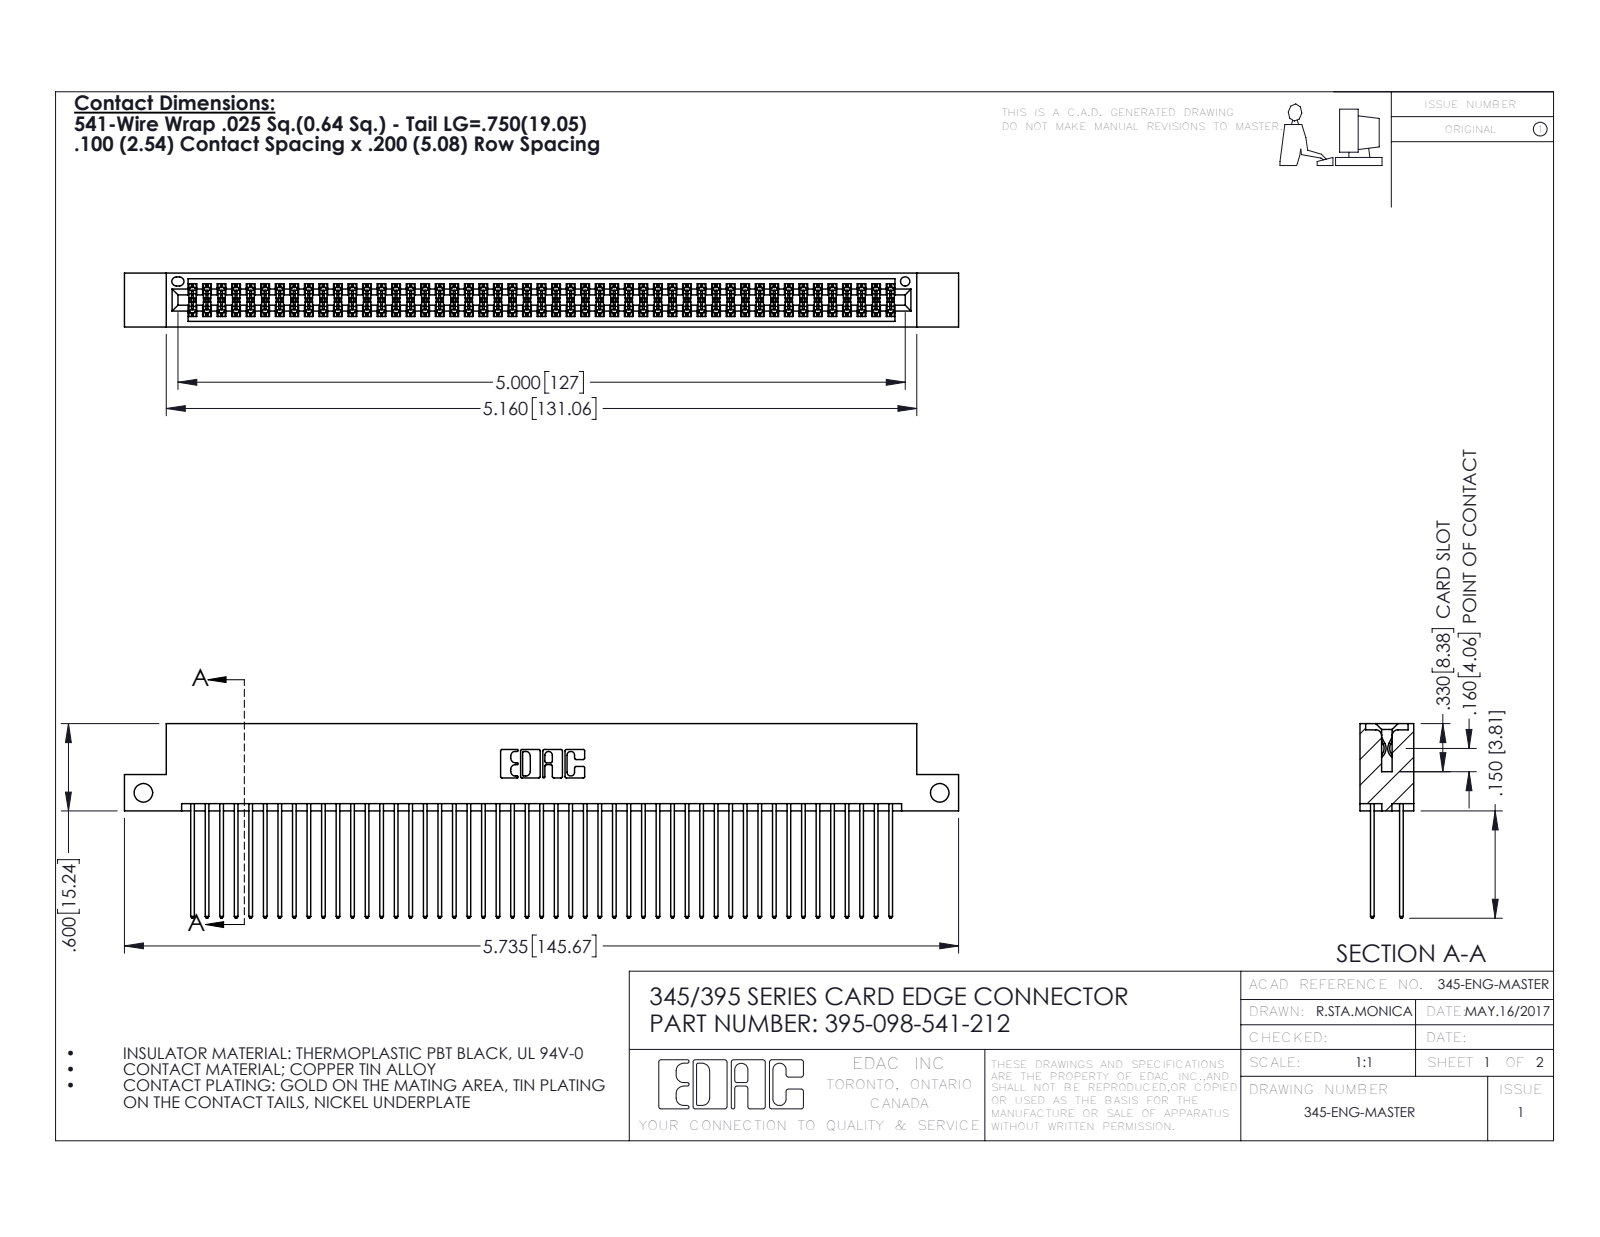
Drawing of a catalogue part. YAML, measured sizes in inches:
part_name: "345-292-001_345-293-141; 345 Part_Flush Mounting Lugs - Side Mount; 395-098-541-212"
step_written_by: "SolidWorks 2016 (CONFIG_CONTROL_DESIGN)"
units: inches
bodies: {solids: 99, faces: 5026, planar: 3314, cylindrical: 1712, other: 0}
overall_size: [5.735, 1.337, 0.37]
volume: 0.896
surface_area: 37.75
round_holes:
  - {diameter: 0.128, count: 2}
  - {diameter: 0.064, count: 1}
partial_cylinders:
  - {radius: 0.006, count: 147}
  - {radius: 0.01, count: 98}
  - {radius: 0.01, count: 22}
  - {radius: 0.007, count: 6}
  - {radius: 0.031, count: 6}
  - {radius: 0.026, count: 3}
  - {radius: 0.014, count: 2}
  - {radius: 0.019, count: 2}
face_to_face_distances: [0.298, 0.072, 0.2, 0.098, 0.272, 0.025, 0.225, 0.37, 0.175, 0.149]
hole_center_spacings: [5.475]
